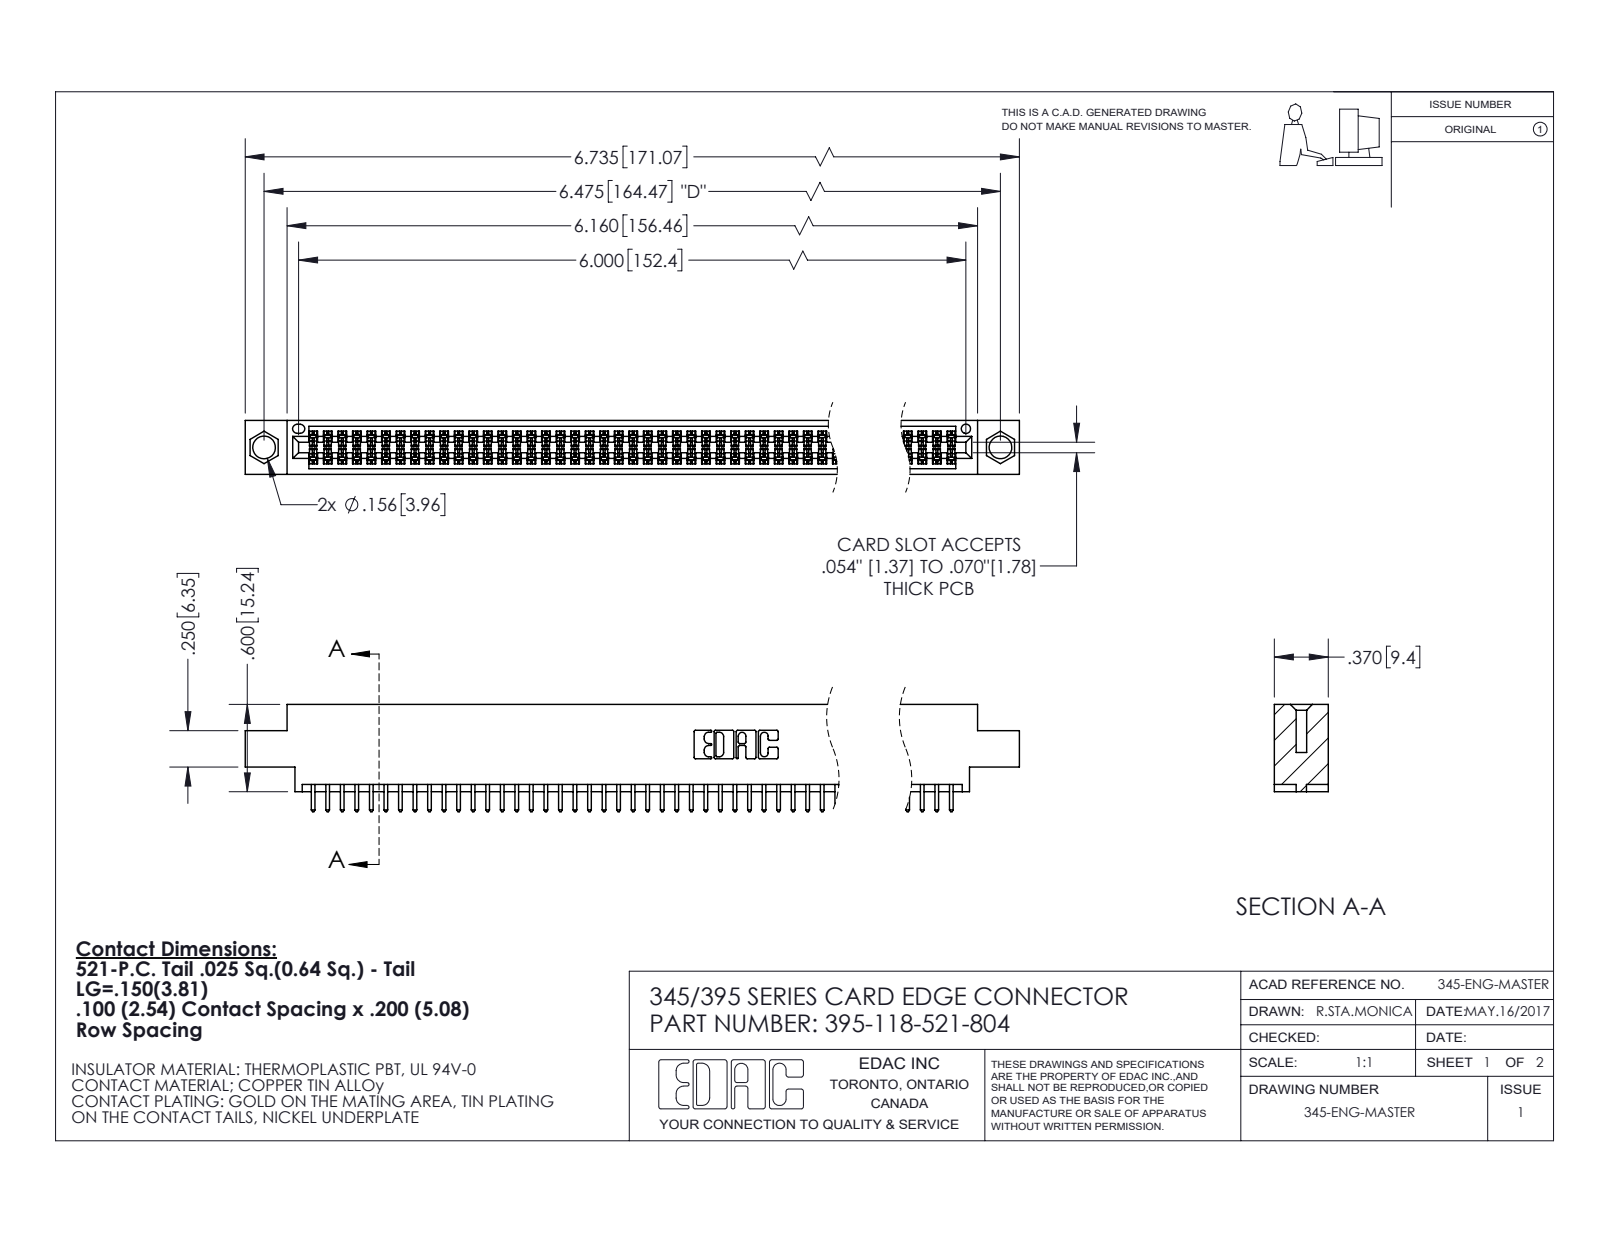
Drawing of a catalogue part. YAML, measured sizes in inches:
part_name: "395-118-521-804; 345 Part_0.170 Offset - 0.156 Dia-TI; 345-292-001_345-293-121"
step_written_by: "SolidWorks 2020 (CONFIG_CONTROL_DESIGN)"
units: inches
bodies: {solids: 119, faces: 6044, planar: 3992, cylindrical: 2052, other: 0}
overall_size: [6.735, 0.737, 0.37]
volume: 1.007
surface_area: 37.84
round_holes:
  - {diameter: 0.156, count: 2}
  - {diameter: 0.064, count: 1}
partial_cylinders:
  - {radius: 0.006, count: 178}
  - {radius: 0.01, count: 118}
  - {radius: 0.01, count: 22}
  - {radius: 0.007, count: 6}
  - {radius: 0.031, count: 6}
  - {radius: 0.026, count: 3}
  - {radius: 0.014, count: 2}
  - {radius: 0.019, count: 2}
face_to_face_distances: [0.072, 0.298, 0.2, 0.37, 0.098, 0.272, 0.025, 0.225, 0.175, 0.149]
hole_center_spacings: [0.27, 6.239, 6.475]
